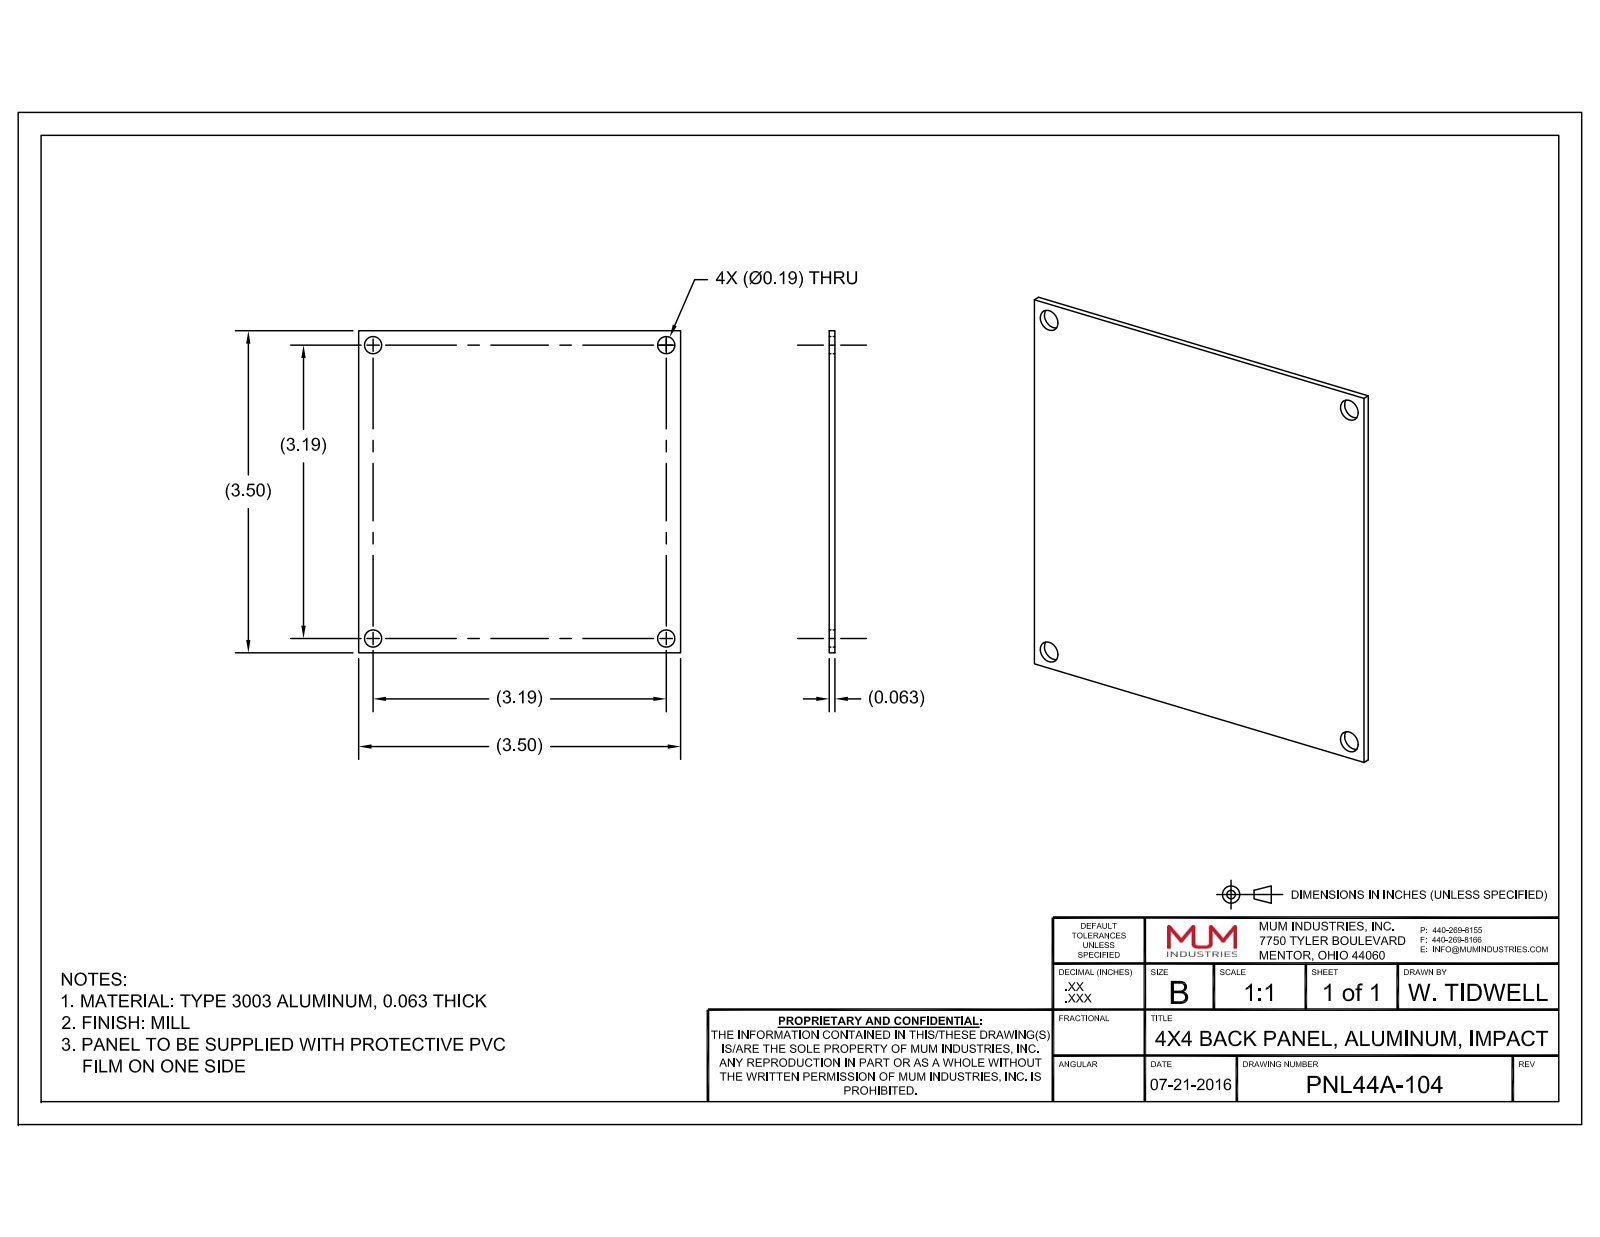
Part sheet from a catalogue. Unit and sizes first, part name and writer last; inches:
Units: inches
Overall size (bounding box): 3.509 × 3.509 × 0.49
Round holes (diameter × count): ⌀0.187 ×4
Round bosses / shafts (diameter × count): ⌀0.322 ×4, ⌀0.164 ×4, ⌀0.119 ×4
Main face-to-face distances: 0.063, 3.5, 0.178, 0.115, 0.112, 0.049, 0.066, 3.14, 0.312, 0.375
Hole centre spacings: 3.187, 4.507
Volume: 0.816 in³ · Surface area: 27.35 in²
Bodies: 5 solids, 422 faces (110 planar, 152 cylindrical, 160 other)
Part name (STEP PRODUCT): PNL44A-104; 9912597-82-10; ABP44-IMP_ASM
STEP written by: CREO PARAMETRIC BY PTC INC, 2016050 (CONFIG_CONTROL_DESIGN)
